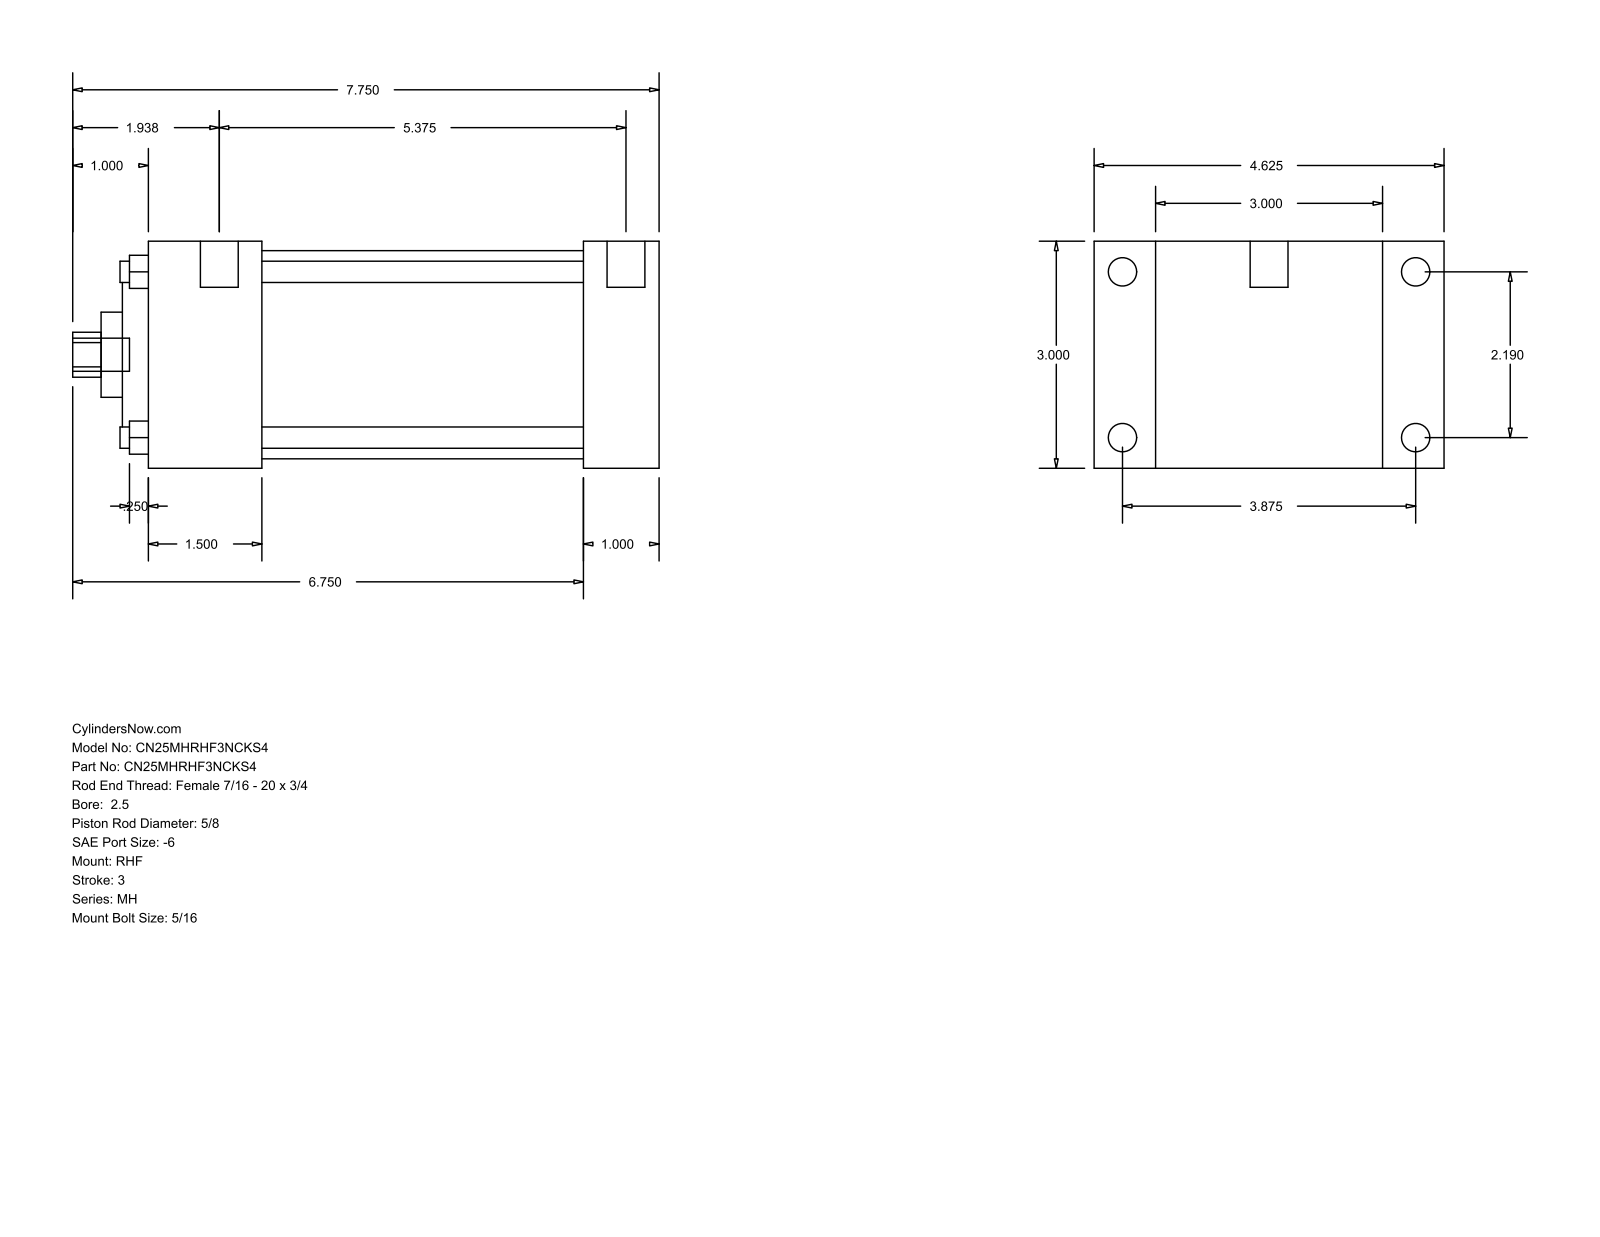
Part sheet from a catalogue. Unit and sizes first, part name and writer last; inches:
Units: inches
Overall size (bounding box): 7.75 × 4.625 × 3
Round holes (diameter × count): ⌀0.281 ×4, ⌀0.625 ×1, ⌀1.125 ×1, ⌀2.187 ×1, ⌀2.75 ×1
Round bosses / shafts (diameter × count): ⌀0.375 ×4, ⌀0.219 ×4, ⌀0.5 ×2, ⌀0.437 ×1
Partial cylindrical surfaces — rounded edges, fillets, slot ends (radius × count): R0.297 ×1
Main face-to-face distances: 3, 1, 0.813, 3.813, 6.75, 5.75, 4.625, 1.5, 4.25, 5.25
Hole centre spacings: 1.548, 2.19, 3.097
Bodies: 0 solids, 90 faces (61 planar, 29 cylindrical, 0 other)
Part name (STEP PRODUCT): MH_RHF__0250_0.625
STEP written by: GSSL Pune (CONFIG_CONTROL_DESIGN)
